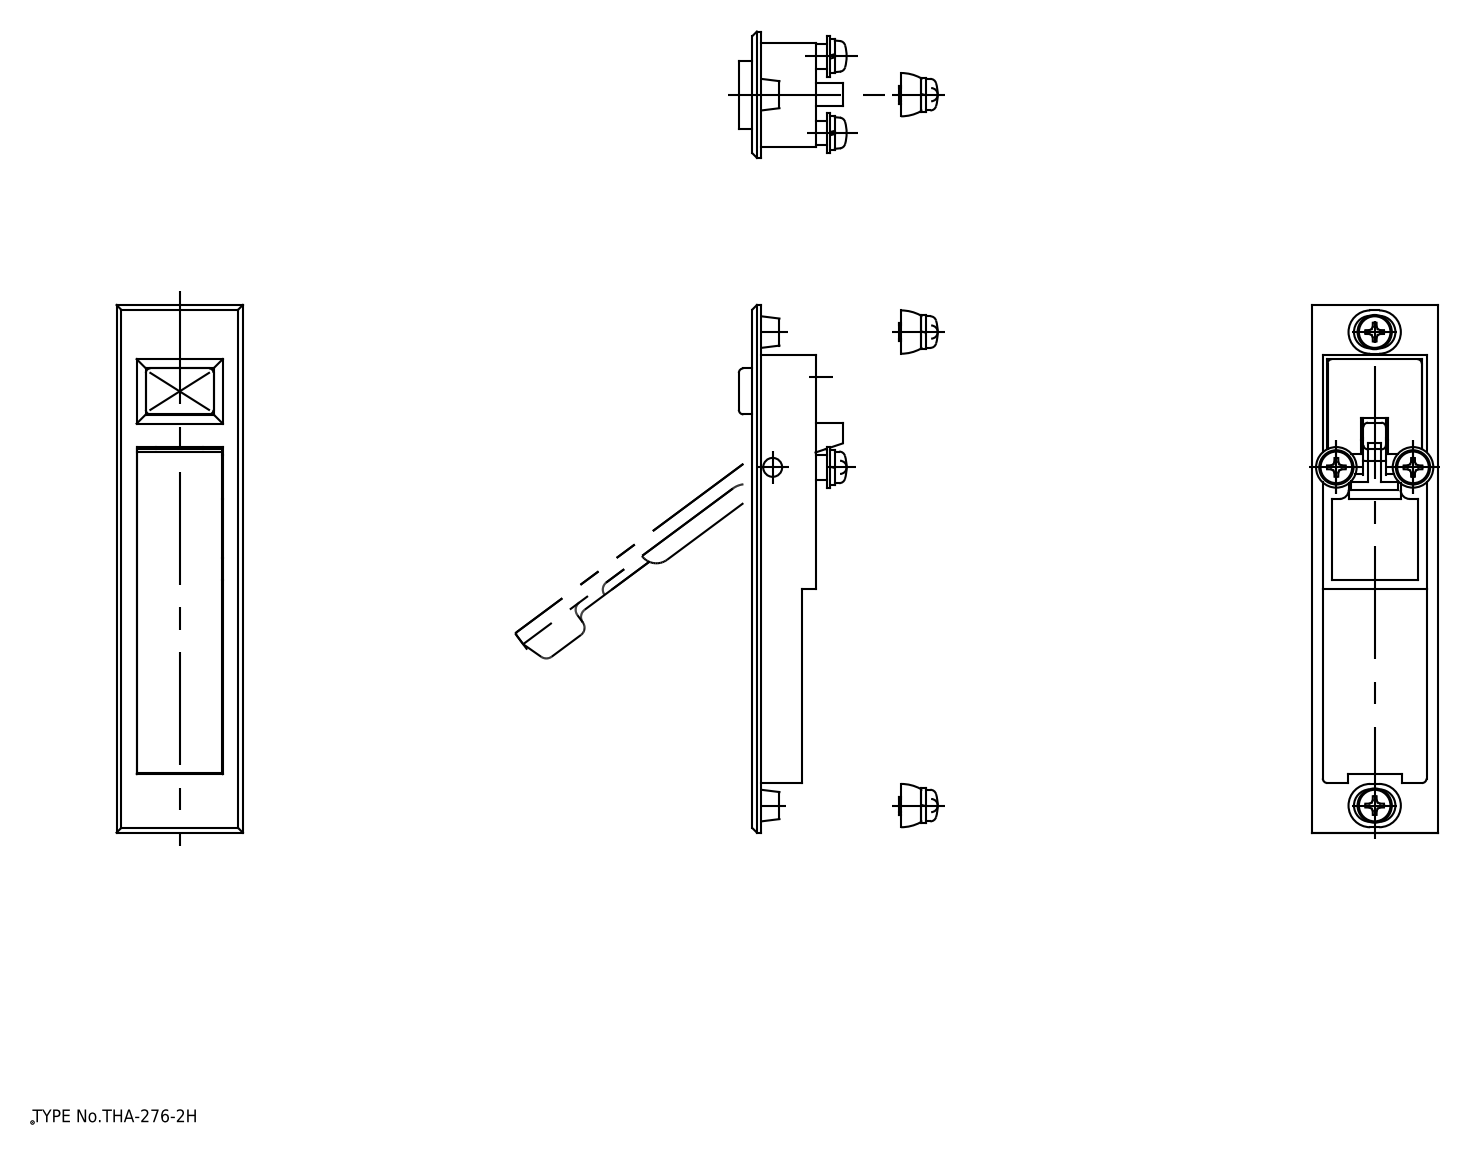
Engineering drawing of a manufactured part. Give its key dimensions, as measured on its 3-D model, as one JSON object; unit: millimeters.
{"part_name": "screw_A; screw_B; bracket; housing (+3 more)", "step_written_by": "spGate 19.8.4 (****-****-****-****) (AUTOMOTIVE_DESIGN)", "units": "millimeters", "bodies": {"solids": 10, "faces": 342, "planar": 214, "cylindrical": 84, "other": 44}, "overall_size": [117, 28, 23.85], "volume_mm3": 25472, "surface_area_mm2": 19999, "round_holes": [[4, 4], [3, 1]], "round_bosses_or_shafts": [[7.6, 4], [9, 2], [5.5, 2]], "partial_cylinders_radius": [[1, 16], [2, 4], [2.1, 4], [8.5, 4], [9, 4], [3, 1], [4, 1], [7, 1]], "face_to_face_distances": [2, 9, 7, 11, 4, 21, 5, 4.5, 2.1, 6], "hole_center_spacings": [31.18, 75.48, 17, 105]}
